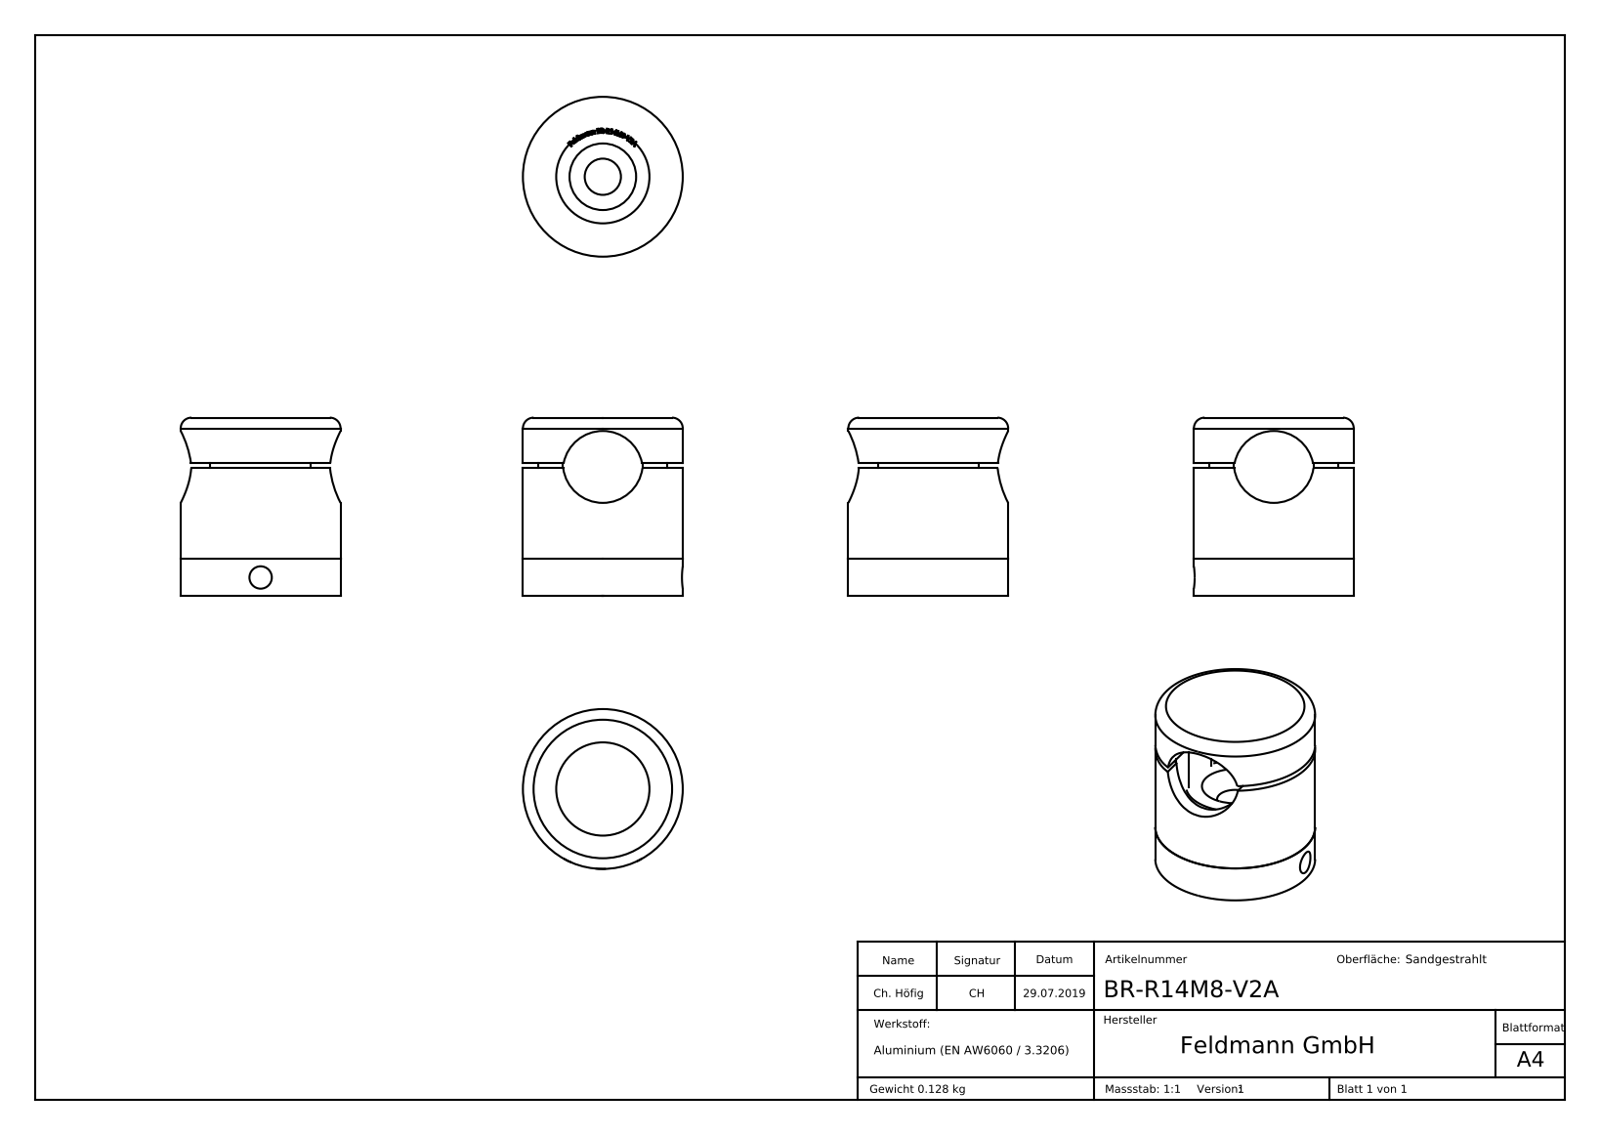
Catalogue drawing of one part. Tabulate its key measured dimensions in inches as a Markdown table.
| quantity | value |
| --- | --- |
| part name | BR-R1XM8-XXX Teil2_BR-R14M8-V2A Teil2; BR-R14M8-V2A; BR-R1XM8-XXX Teil3_BR-R14M8-V2A Teil3; BR-R1XM8-XXX Teil1_BR-1XM8-V2A Teil1 (+3 more) |
| STEP written by | SolidWorks 2015 (CONFIG_CONTROL_DESIGN) |
| units | inches |
| bodies | 3 solids, 322 faces (185 planar, 15 cylindrical, 122 other) |
| overall size | 2.533 × 1.181 × 1.181 |
| volume | 0.99 in³ |
| surface area | 14.99 in² |
| round holes (diameter × count) | 0.165 × 1, 0.268 × 1, 0.492 × 1, 0.953 × 1 |
| round bosses / shafts (diameter × count) | 1.181 × 1, 0.787 × 1 |
| partial cylindrical surfaces (radius × count) | 0.295 × 2, 0.344 × 1, 0.474 × 1 |
| main face-to-face distances | 0.276, 1.319, 1.043, 0.354, 0.335, 0.689, 0.984, 0.709, 0.591, 0.945 |
